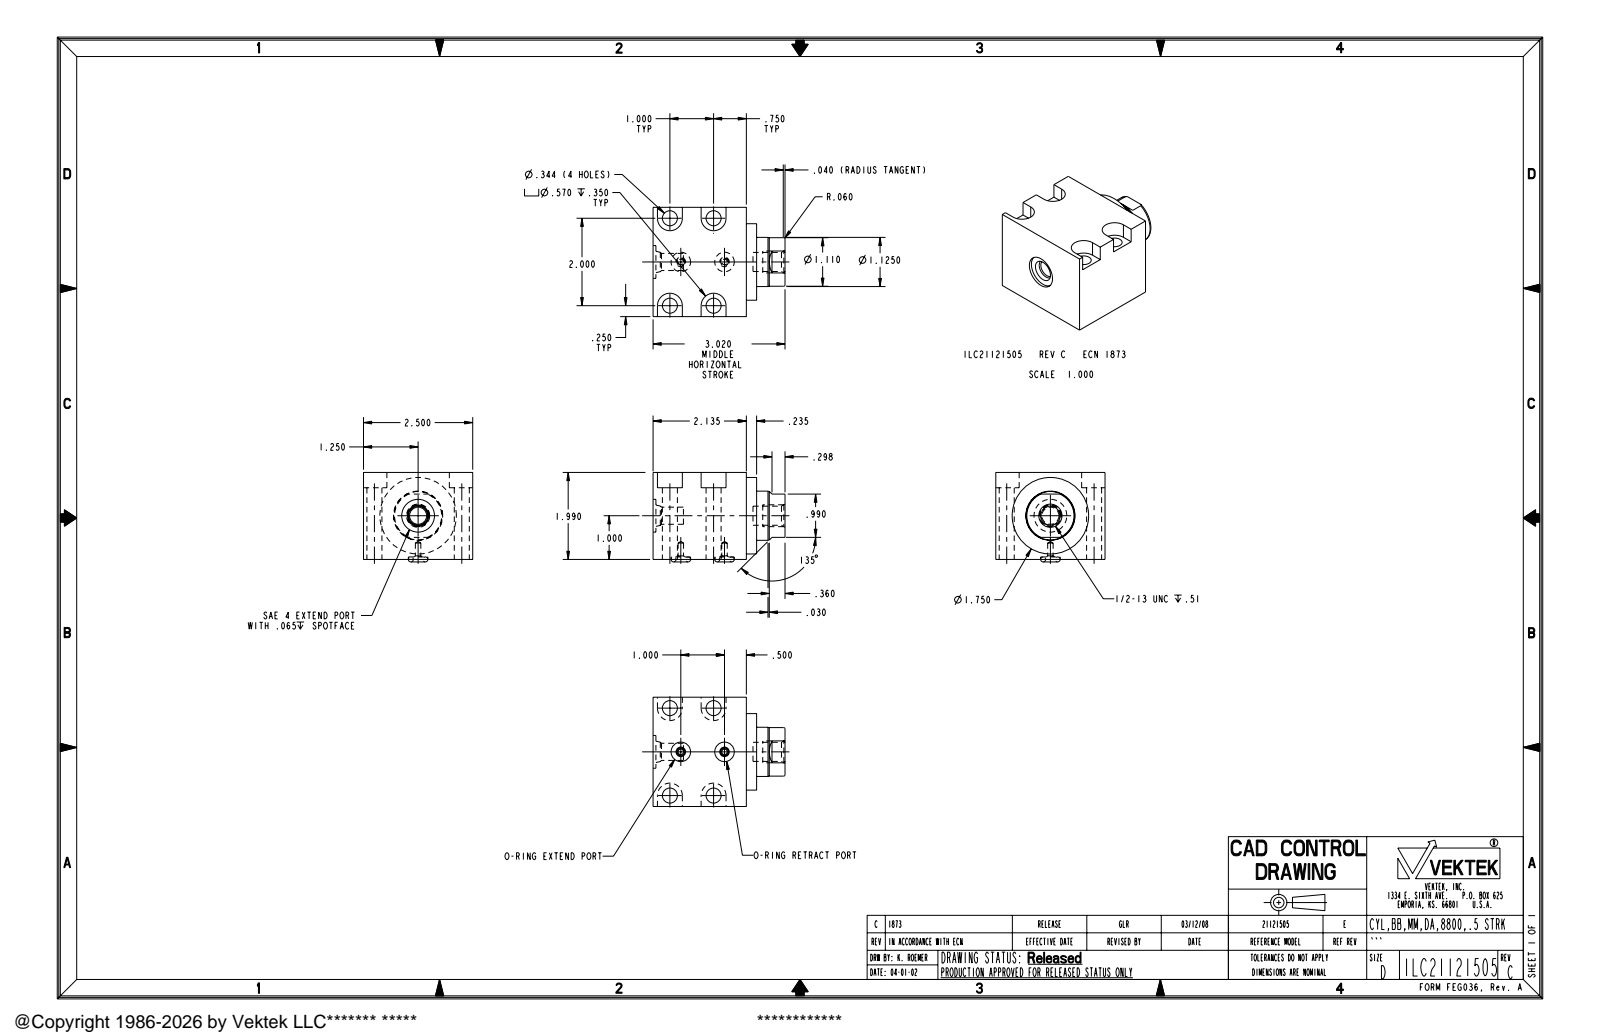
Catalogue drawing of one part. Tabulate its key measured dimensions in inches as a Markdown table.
| quantity | value |
| --- | --- |
| part name | ILC21121505 |
| STEP written by | PRO/ENGINEER BY PARAMETRIC TECHNOLOGY CORPORATION, 2007460 (AUTOMOTIVE_DESIGN_CC2) |
| units | inches |
| bodies | 1 solid, 90 faces (30 planar, 34 cylindrical, 26 other) |
| overall size | 3.02 × 2.5 × 2.047 |
| volume | 10.59 in³ |
| surface area | 43.94 in² |
| round holes (diameter × count) | 0.344 × 4, 0.125 × 2, 0.447 × 2, 0.392 × 1, 0.437 × 1, 0.75 × 1 |
| round bosses / shafts (diameter × count) | 1.75 × 1, 1.125 × 1, 1.11 × 1, 0.5 × 1 |
| partial cylindrical surfaces (radius × count) | 0.285 × 4 |
| main face-to-face distances | 1.99, 2.5, 2.135, 0.235, 2.37, 1.64, 0.35, 0.65, 0.885, 3.02 |
| hole center spacings | 1.031, 1, 1.25, 1.601, 2, 2.236 |
